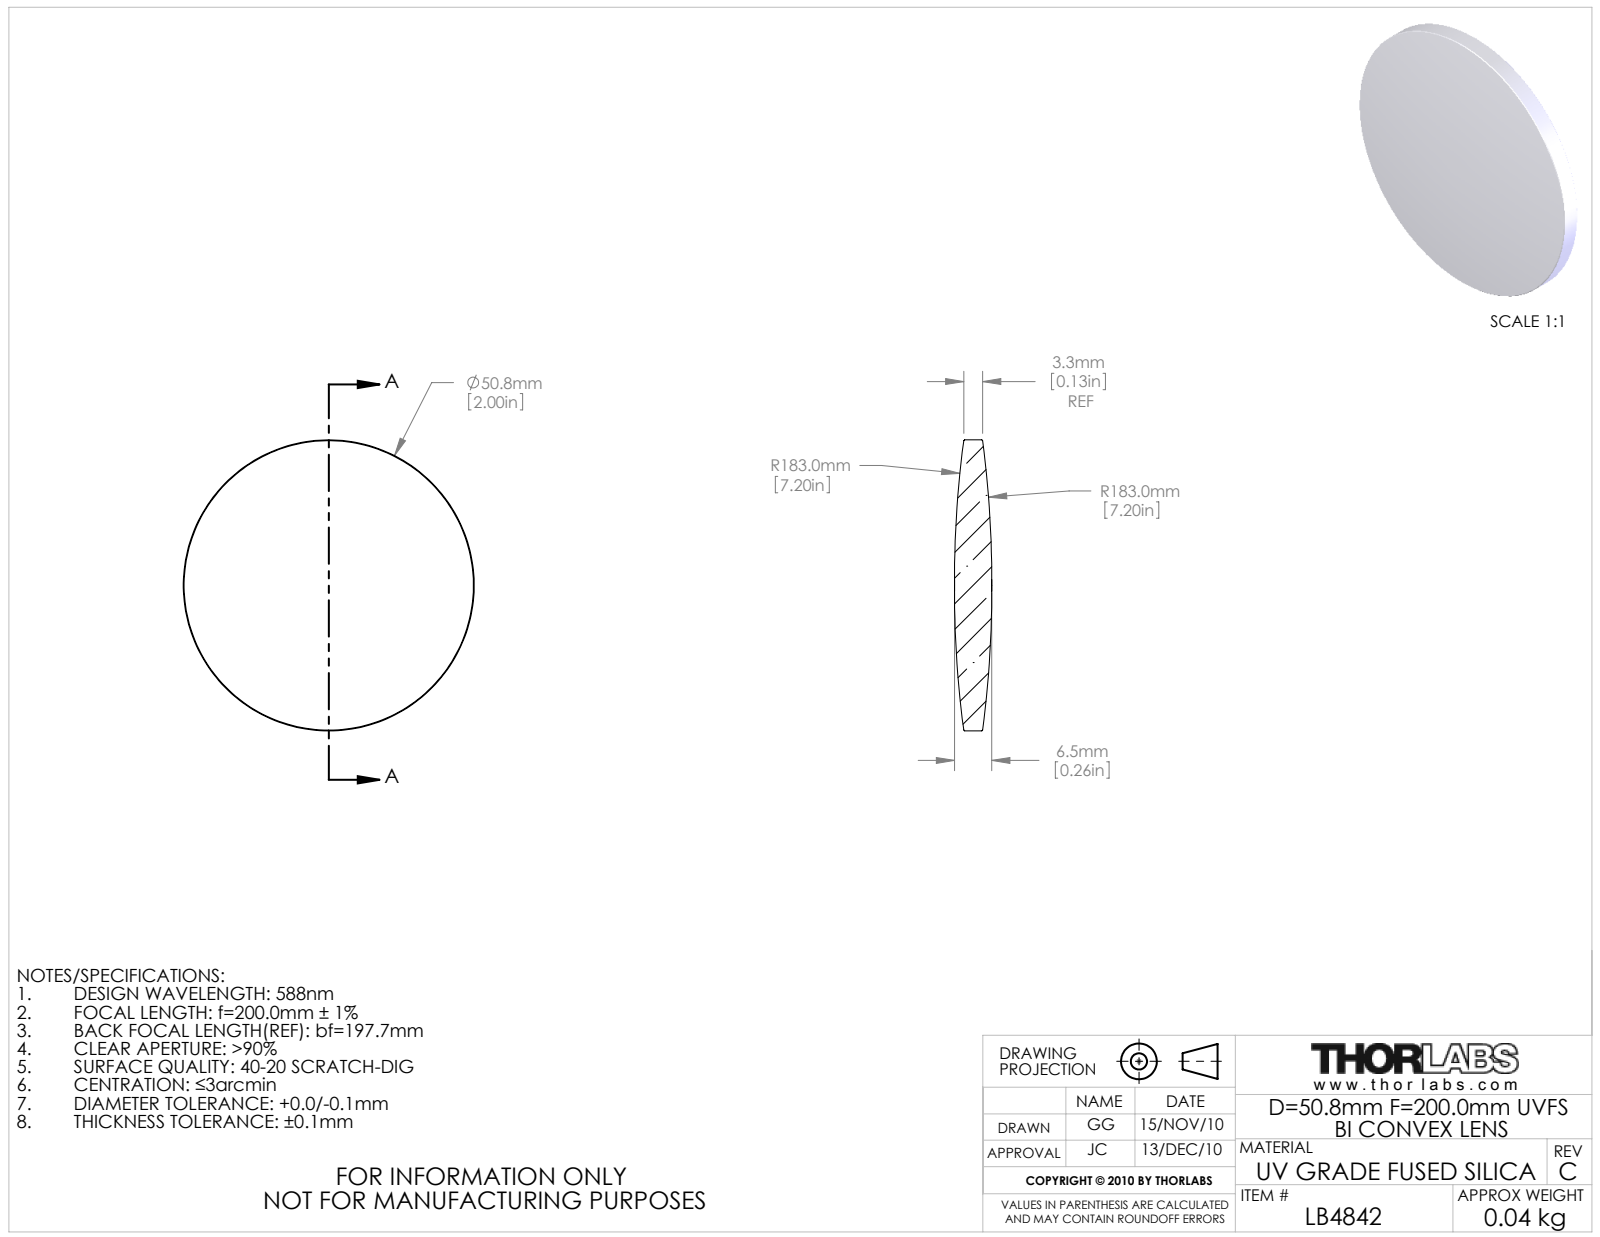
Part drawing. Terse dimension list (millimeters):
name: 3417-E0W
written by: SolidWorks 2009 (AUTOMOTIVE_DESIGN)
unit: mm
bodies: 1 solid, 10 faces (0 planar, 2 cylindrical, 8 other)
size: 50.8 × 50.8 × 6.51
volume: 9 974 mm³; area: 4 568 mm²
bosses: 1× ⌀50.8
